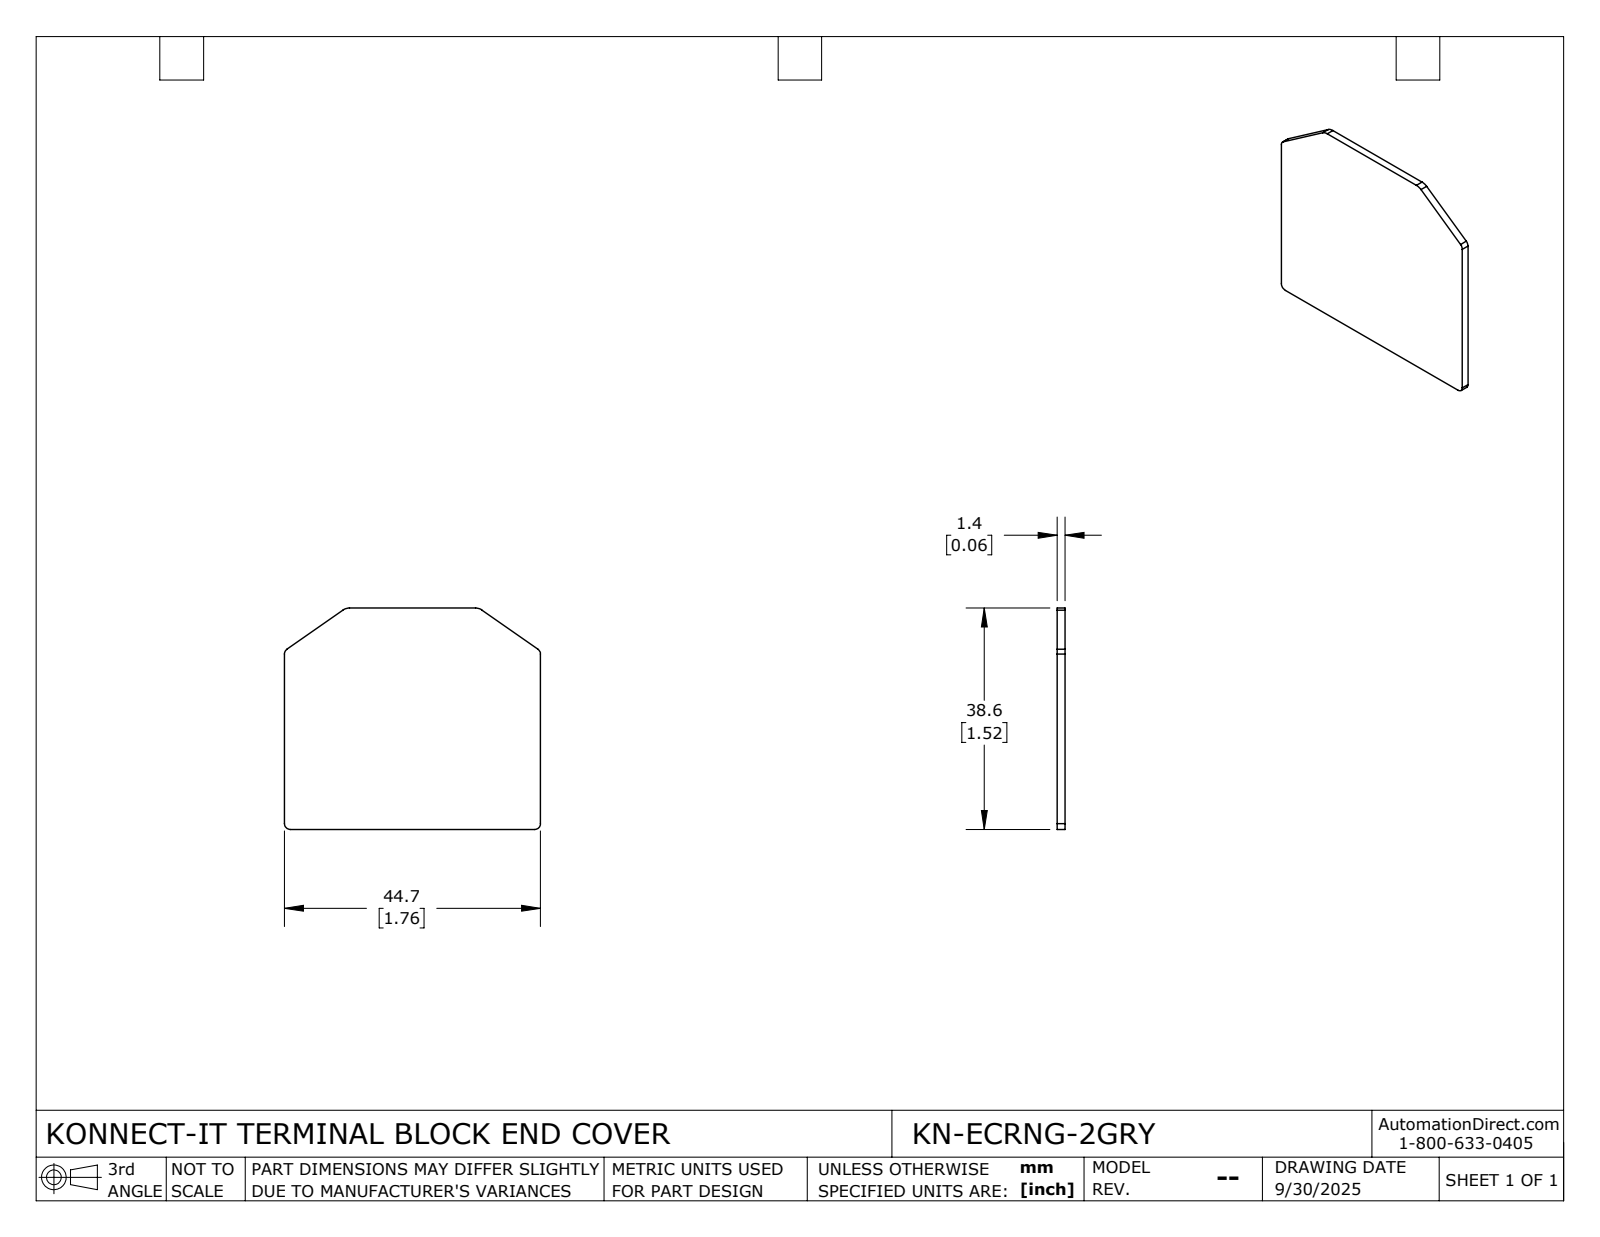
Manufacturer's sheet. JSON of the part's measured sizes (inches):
{"part_name": "KN-ECRNG-2GRY", "step_written_by": "SolidWorks 2024 (CONFIG_CONTROL_DESIGN)", "units": "inches", "bodies": {"solids": 1, "faces": 14, "planar": 8, "cylindrical": 6, "other": 0}, "overall_size": [1.76, 1.521, 0.055], "volume_in3": 0.141, "surface_area_in2": 5.441, "partial_cylinders_radius": [[0.039, 4], [0.079, 2]], "face_to_face_distances": [0.055, 1.76, 1.521]}
